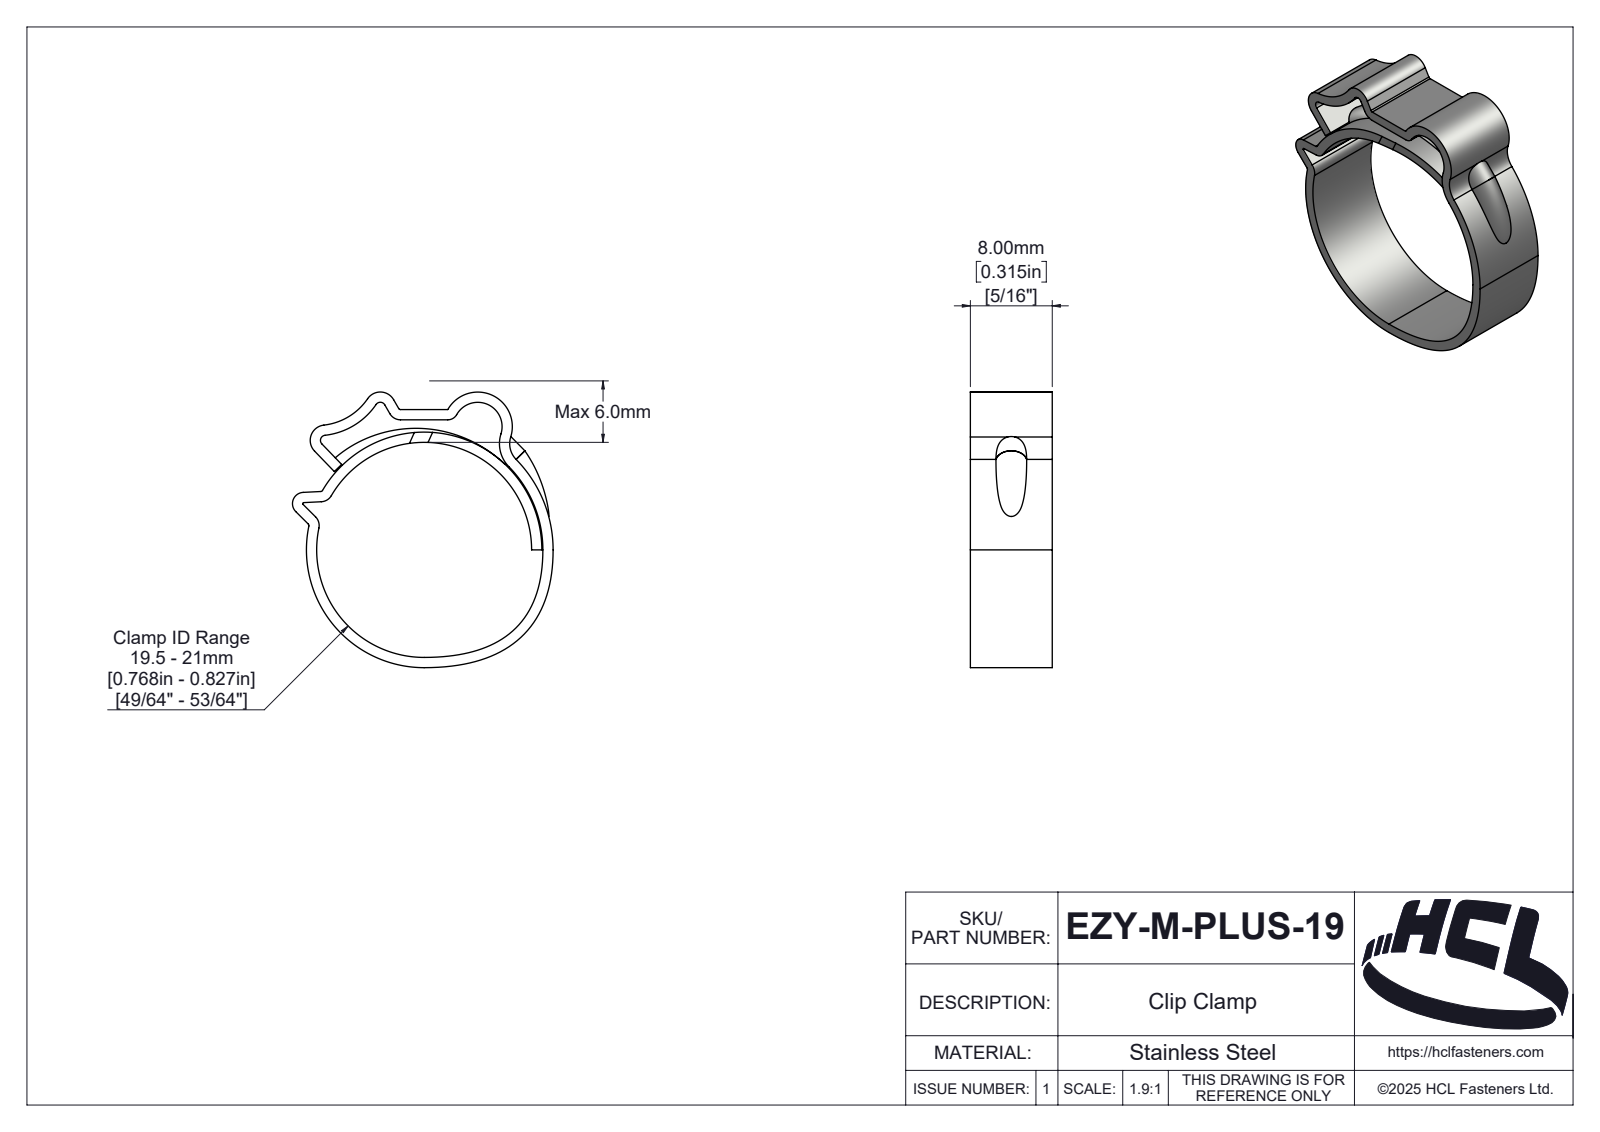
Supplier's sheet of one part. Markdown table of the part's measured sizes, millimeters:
| quantity | value |
| --- | --- |
| part name | EZY-M-PLUS-19 |
| STEP written by | SolidWorks 2025 (AUTOMOTIVE_DESIGN) |
| units | millimeters |
| bodies | 2 solids, 171 faces (21 planar, 86 cylindrical, 64 other) |
| overall size | 26.91 × 25.46 × 8 |
| volume | 886 mm³ |
| surface area | 2 010 mm² |
| partial cylindrical surfaces (radius × count) | 0.2 × 3, 1.2 × 3, 0.5 × 2, 1.5 × 2, 10 × 2, 0.1 × 1, 0.23 × 1, 0.94 × 1 |
| main face-to-face distances | 8, 1, 12.7, 13.7 |
